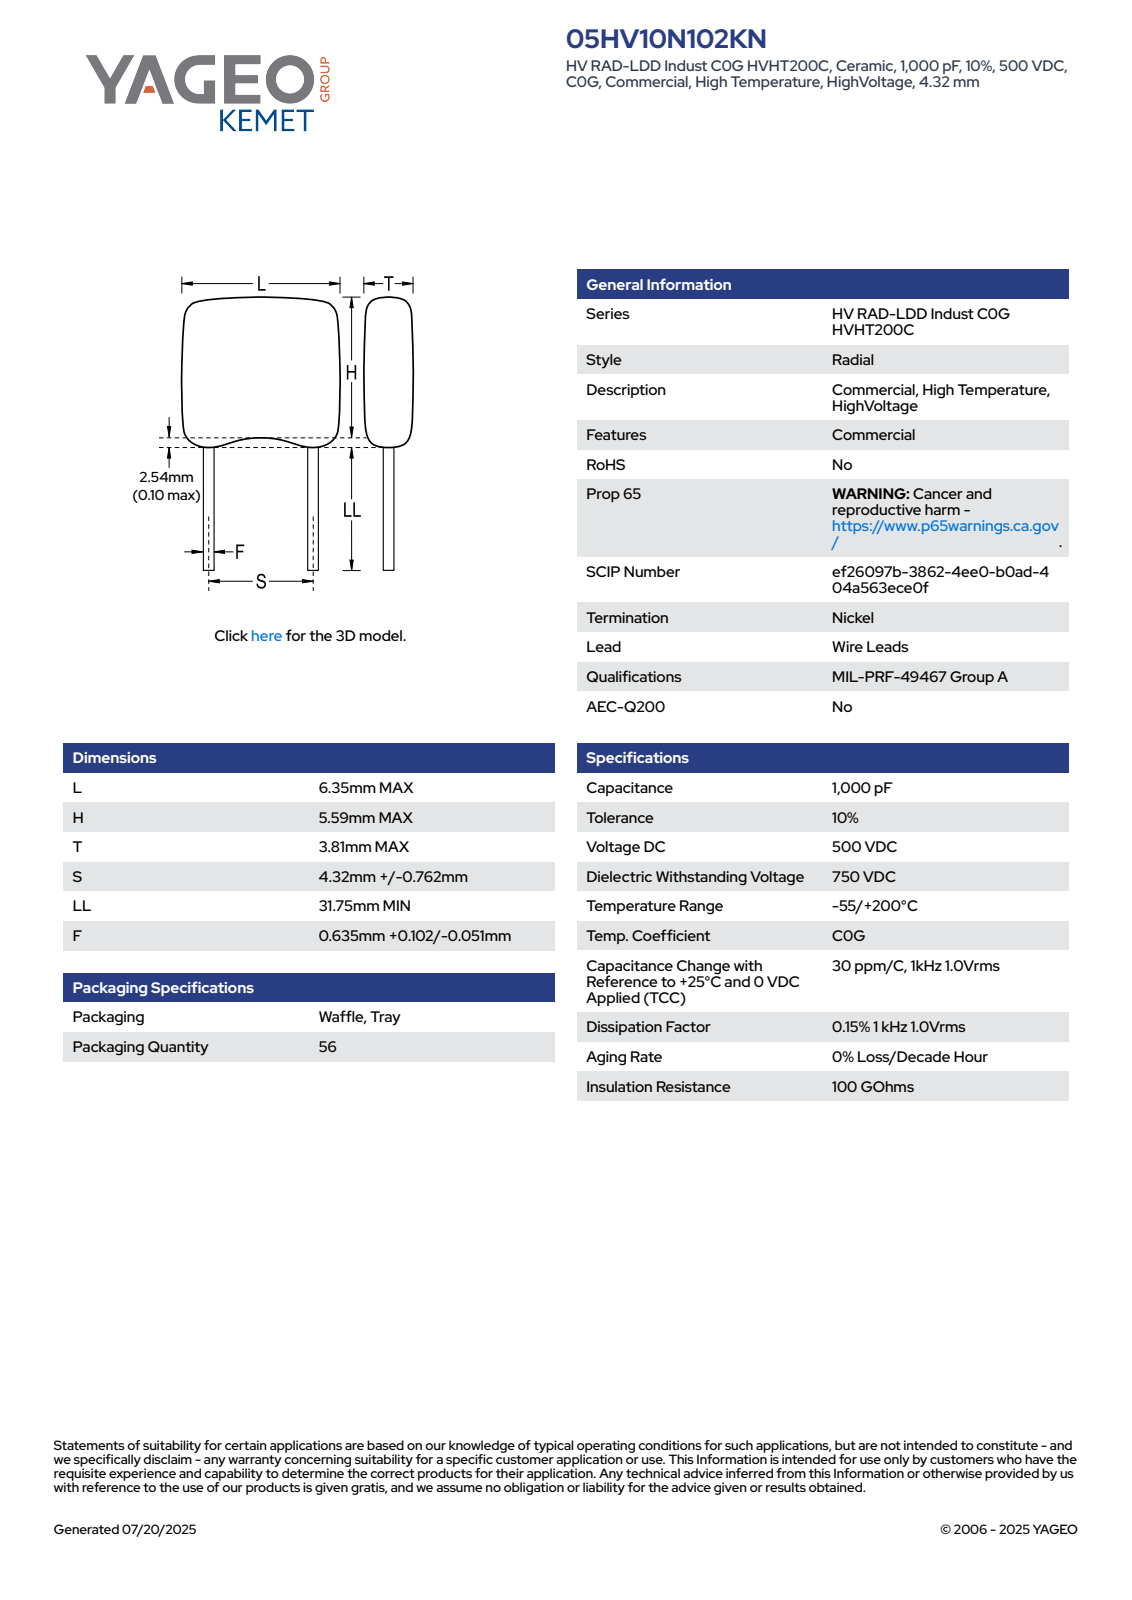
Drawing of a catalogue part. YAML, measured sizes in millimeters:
part_name: "CCRM_RCST_HV10_L6.35H5.59T3.81S4.32LL3.175F0.737"
step_written_by: "SolidWorks 2021 (AUTOMOTIVE_DESIGN)"
units: millimeters
bodies: {solids: 4, faces: 92, planar: 66, cylindrical: 16, other: 10}
overall_size: [38.86, 6.35, 5.08]
volume: 207
surface_area: 325
round_bosses_or_shafts:
  - {diameter: 0.64, count: 2}
partial_cylinders:
  - {radius: 0.5, count: 8}
  - {radius: 2, count: 4}
face_to_face_distances: [6.35, 5.08, 7.11, 31.75, 38.86, 3.05, 4.06, 1.01, 35.81, 34.8]
